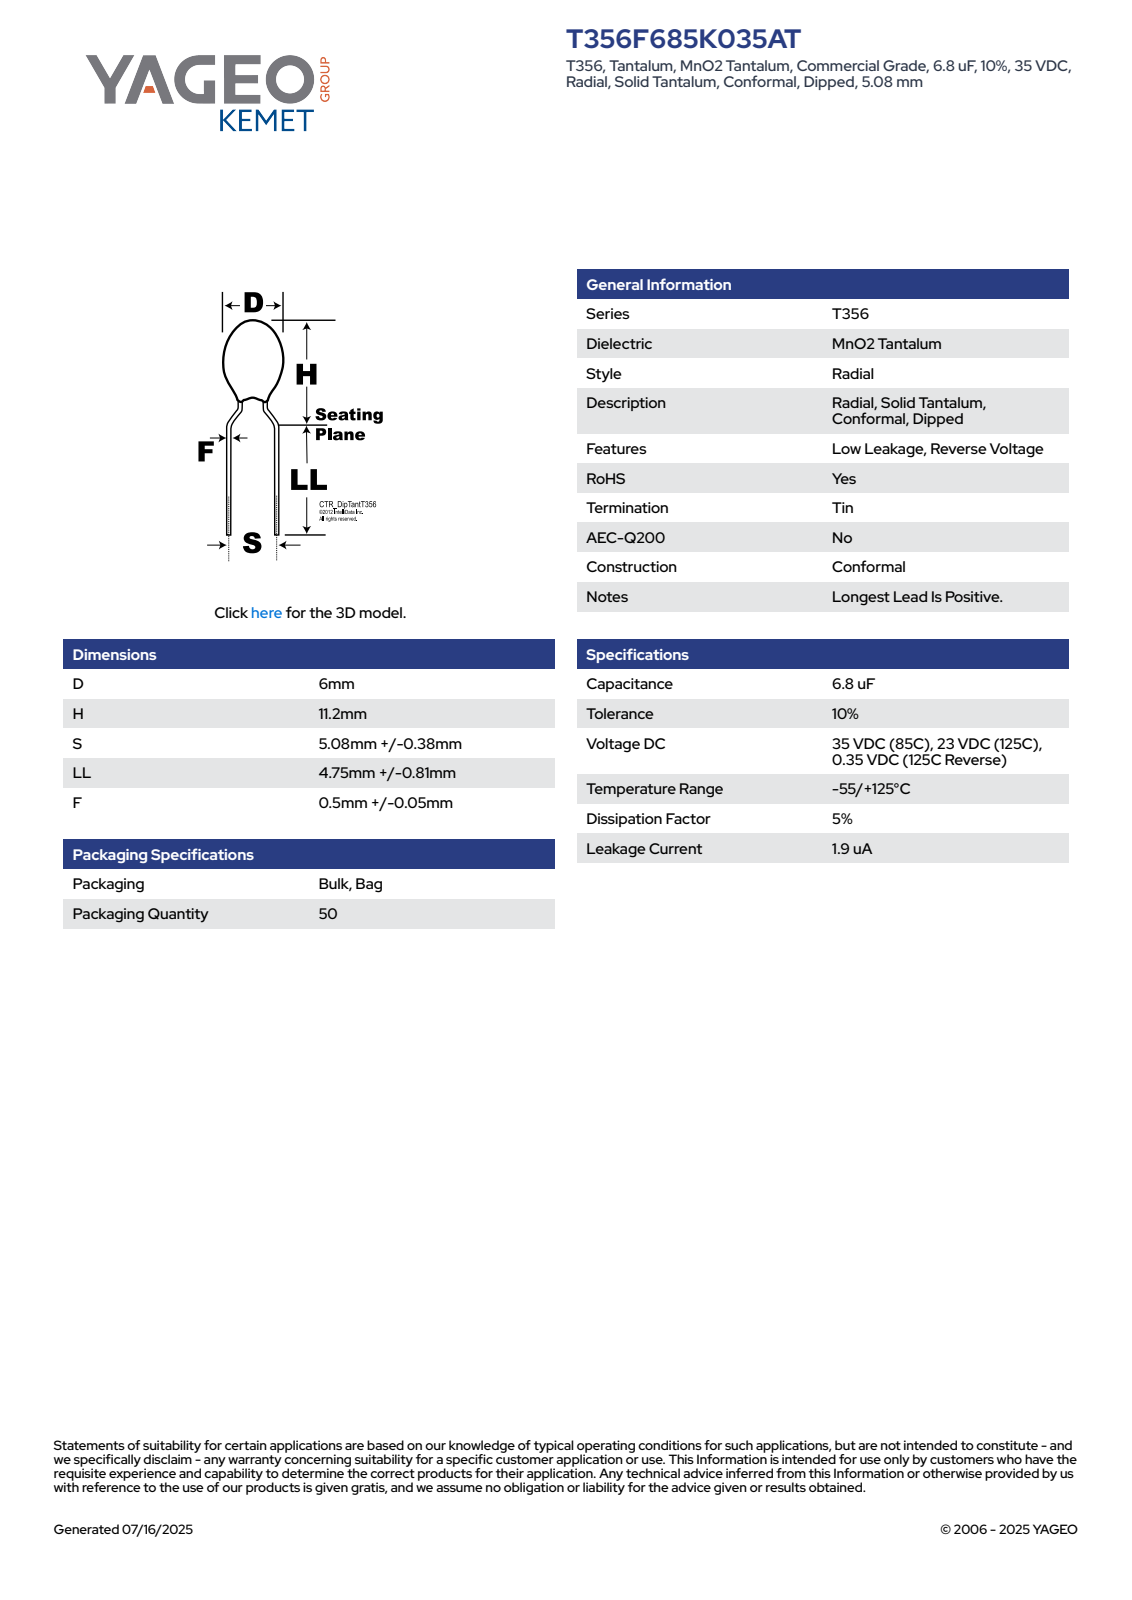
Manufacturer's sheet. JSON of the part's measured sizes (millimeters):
{"part_name": "CTR_T356_D6H11.2S5.08LL5.56F0.55", "step_written_by": "SolidWorks 2014 (AUTOMOTIVE_DESIGN)", "units": "millimeters", "bodies": {"solids": 1, "faces": 100, "planar": 27, "cylindrical": 18, "other": 55}, "overall_size": [16.76, 6, 6], "volume_mm3": 201, "surface_area_mm2": 206, "round_bosses_or_shafts": [[0.55, 6], [6, 1]], "partial_cylinders_radius": [[2.99, 1]], "face_to_face_distances": [7.81, 8.95, 16.76, 14.06, 5.11, 2.7, 13.15, 4.2, 0.91, 3.61]}
